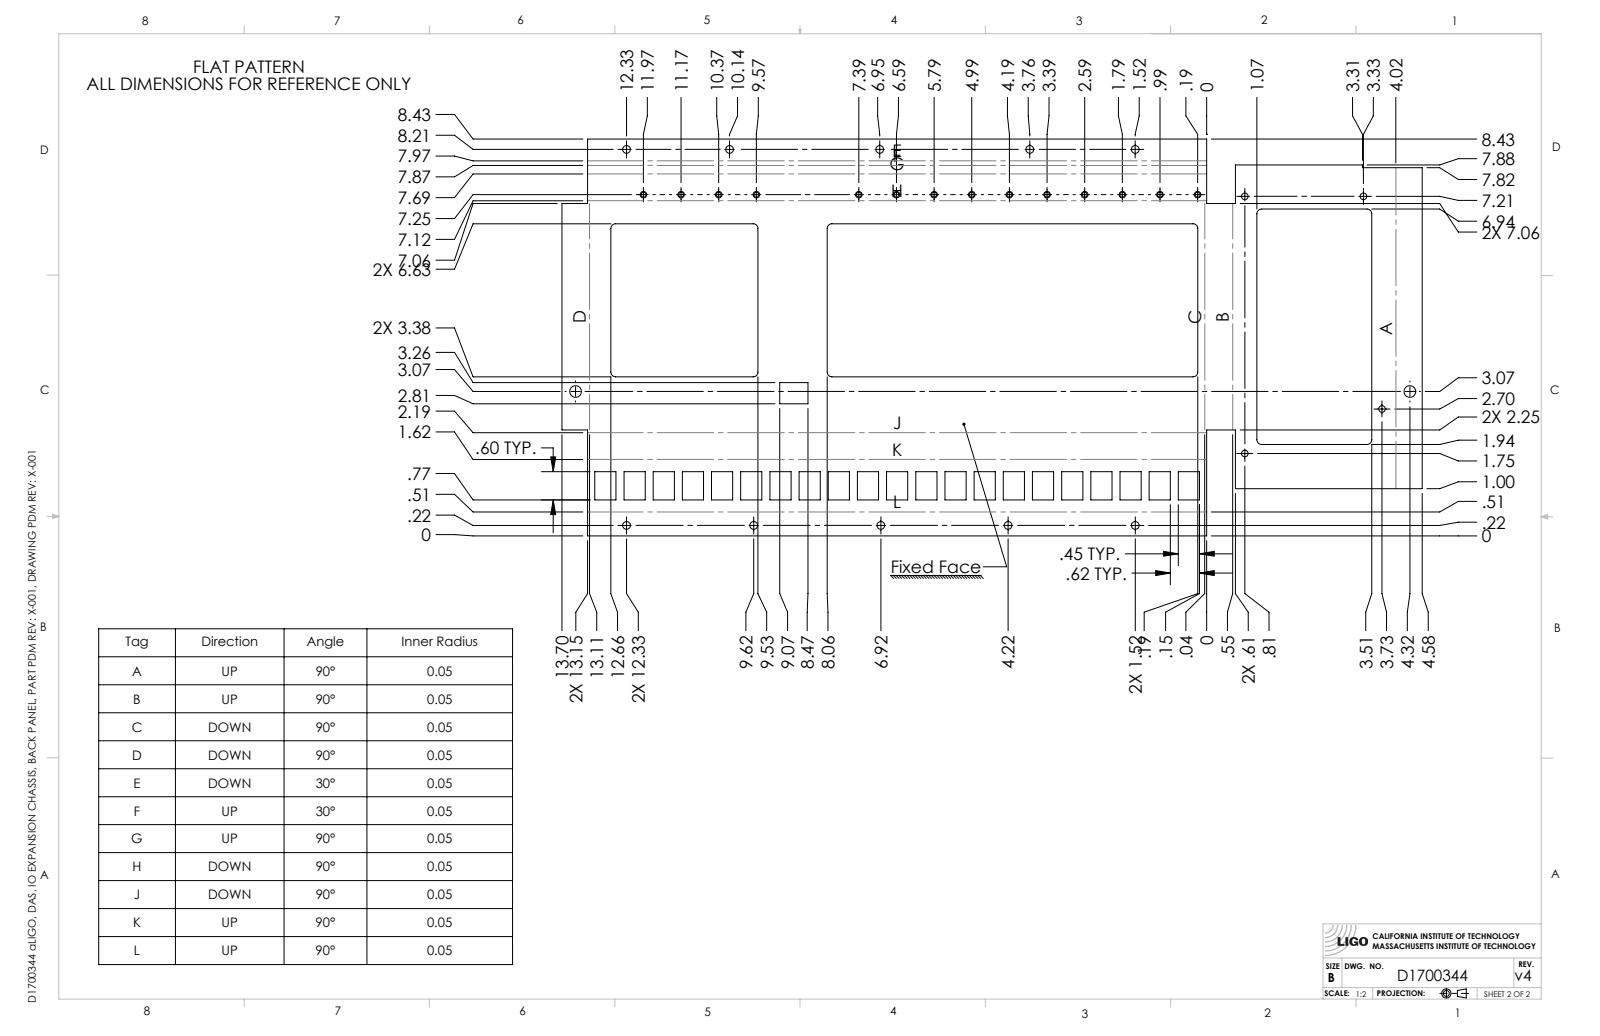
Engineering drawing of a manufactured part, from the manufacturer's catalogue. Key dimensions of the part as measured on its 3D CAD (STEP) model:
Part name (STEP PRODUCT): D1700344-v4
STEP written by: SolidWorks 2017 (CONFIG_CONTROL_DESIGN)
Units: inches
Bodies: 1 solid, 244 faces (180 planar, 60 cylindrical, 4 other)
Overall size (bounding box): 16.654 × 6.875 × 0.673
Volume: 4.266 in³ · Surface area: 186.5 in²
Round holes (diameter × count): ⌀0.107 ×14, ⌀0.166 ×10, ⌀0.25 ×1
Partial cylindrical surfaces — rounded edges, fillets, slot ends (radius × count): R0.1 ×12, R0.05 ×11, R0.098 ×11
Main face-to-face distances: 0.048, 0.625, 0.6, 0.025, 0.048, 1.148, 0.05, 0.55, 0.075, 0.578
Hole centre spacings: 0.8, 1.6, 2.4, 3.2, 4, 4.576, 4.8, 5.376
